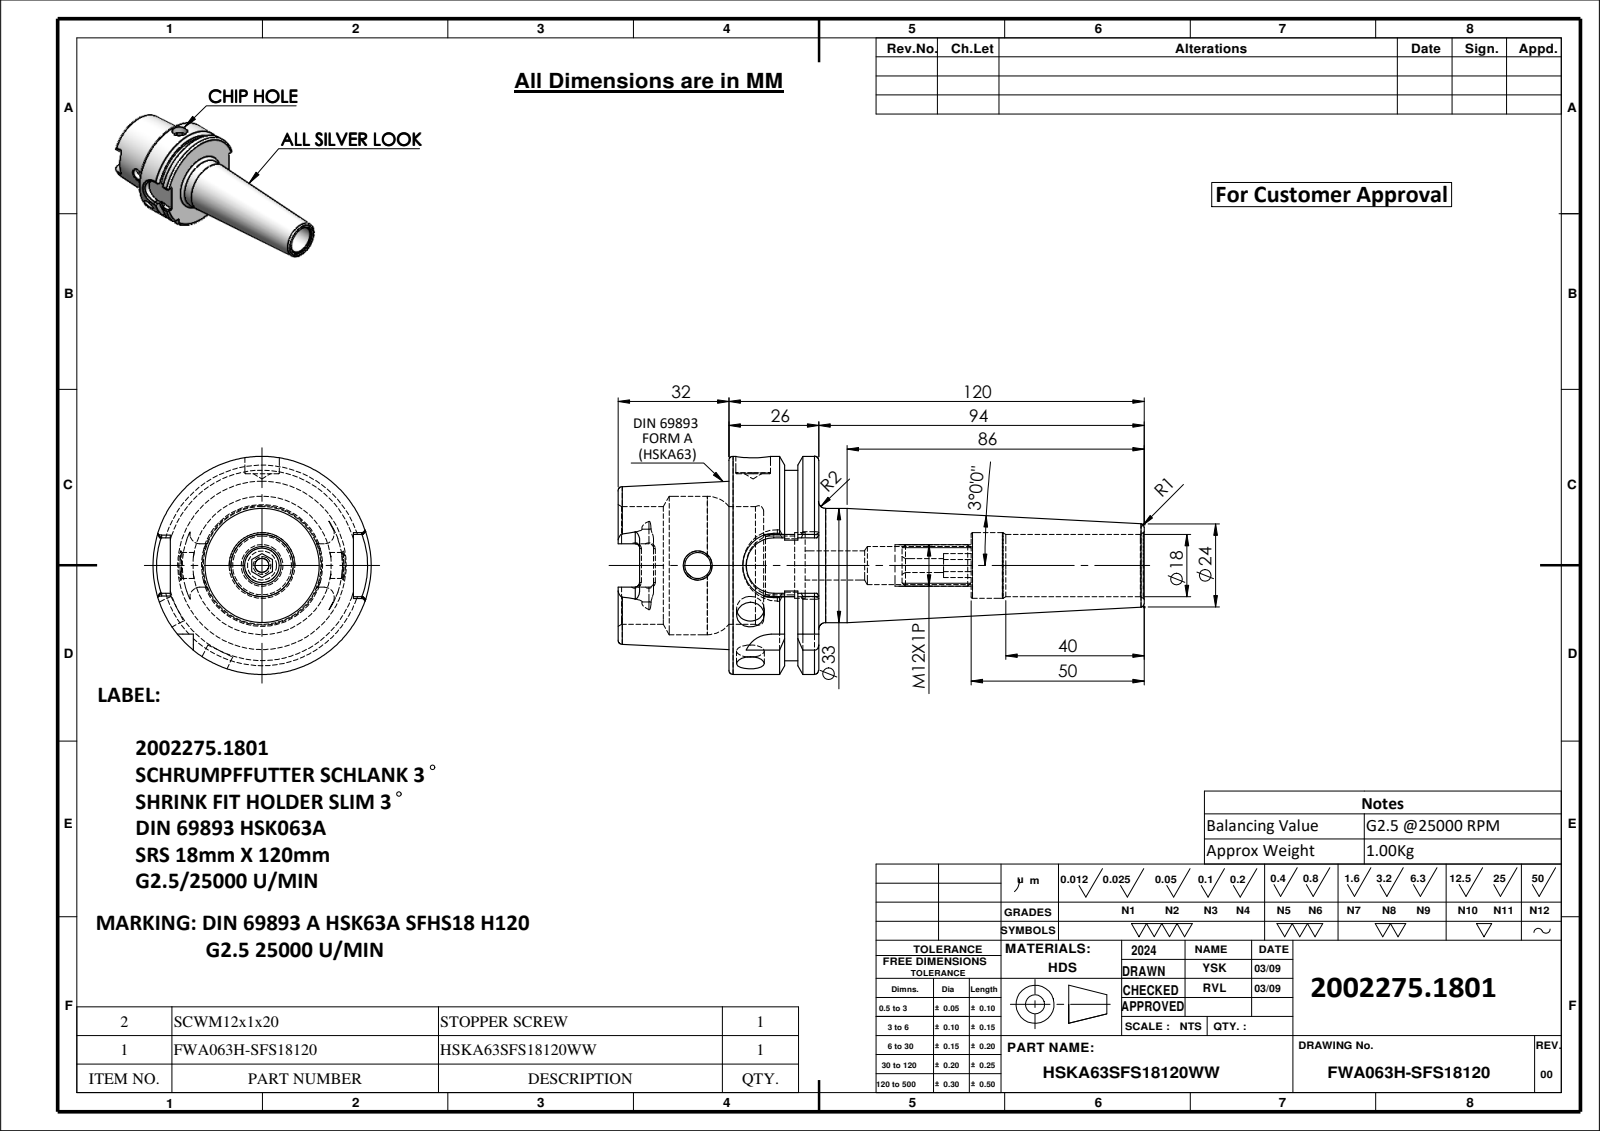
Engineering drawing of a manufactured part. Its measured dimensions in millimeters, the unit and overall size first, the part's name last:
Units: millimetres
Overall size (bounding box): 152 × 63 × 63
Round holes (diameter × count): ⌀8 ×2, ⌀4 ×1, ⌀7.5 ×1, ⌀8.4 ×1, ⌀10 ×1, ⌀11 ×1, ⌀17 ×1, ⌀18 ×1, ⌀19 ×1, ⌀34 ×1, ⌀40 ×1
Round bosses / shafts (diameter × count): ⌀63 ×1, ⌀55 ×1, ⌀33 ×1, ⌀12 ×1
Partial cylindrical surfaces — rounded edges, fillets, slot ends (radius × count): R1.3 ×6, R2.88 ×4, R8 ×2, R9 ×1
Main face-to-face distances: 25.95, 10, 15.95, 32, 42, 57.95, 52.9, 70, 12, 54
Volume: 128 278 mm³ · Surface area: 35 836 mm²
Bodies: 2 solids, 196 faces (59 planar, 57 cylindrical, 80 other)
Part name (STEP PRODUCT): HSKA63SFS18120WW; FWA063H-SFS18120; SCWM12X1P
STEP written by: SolidWorks 2024 (CONFIG_CONTROL_DESIGN)
